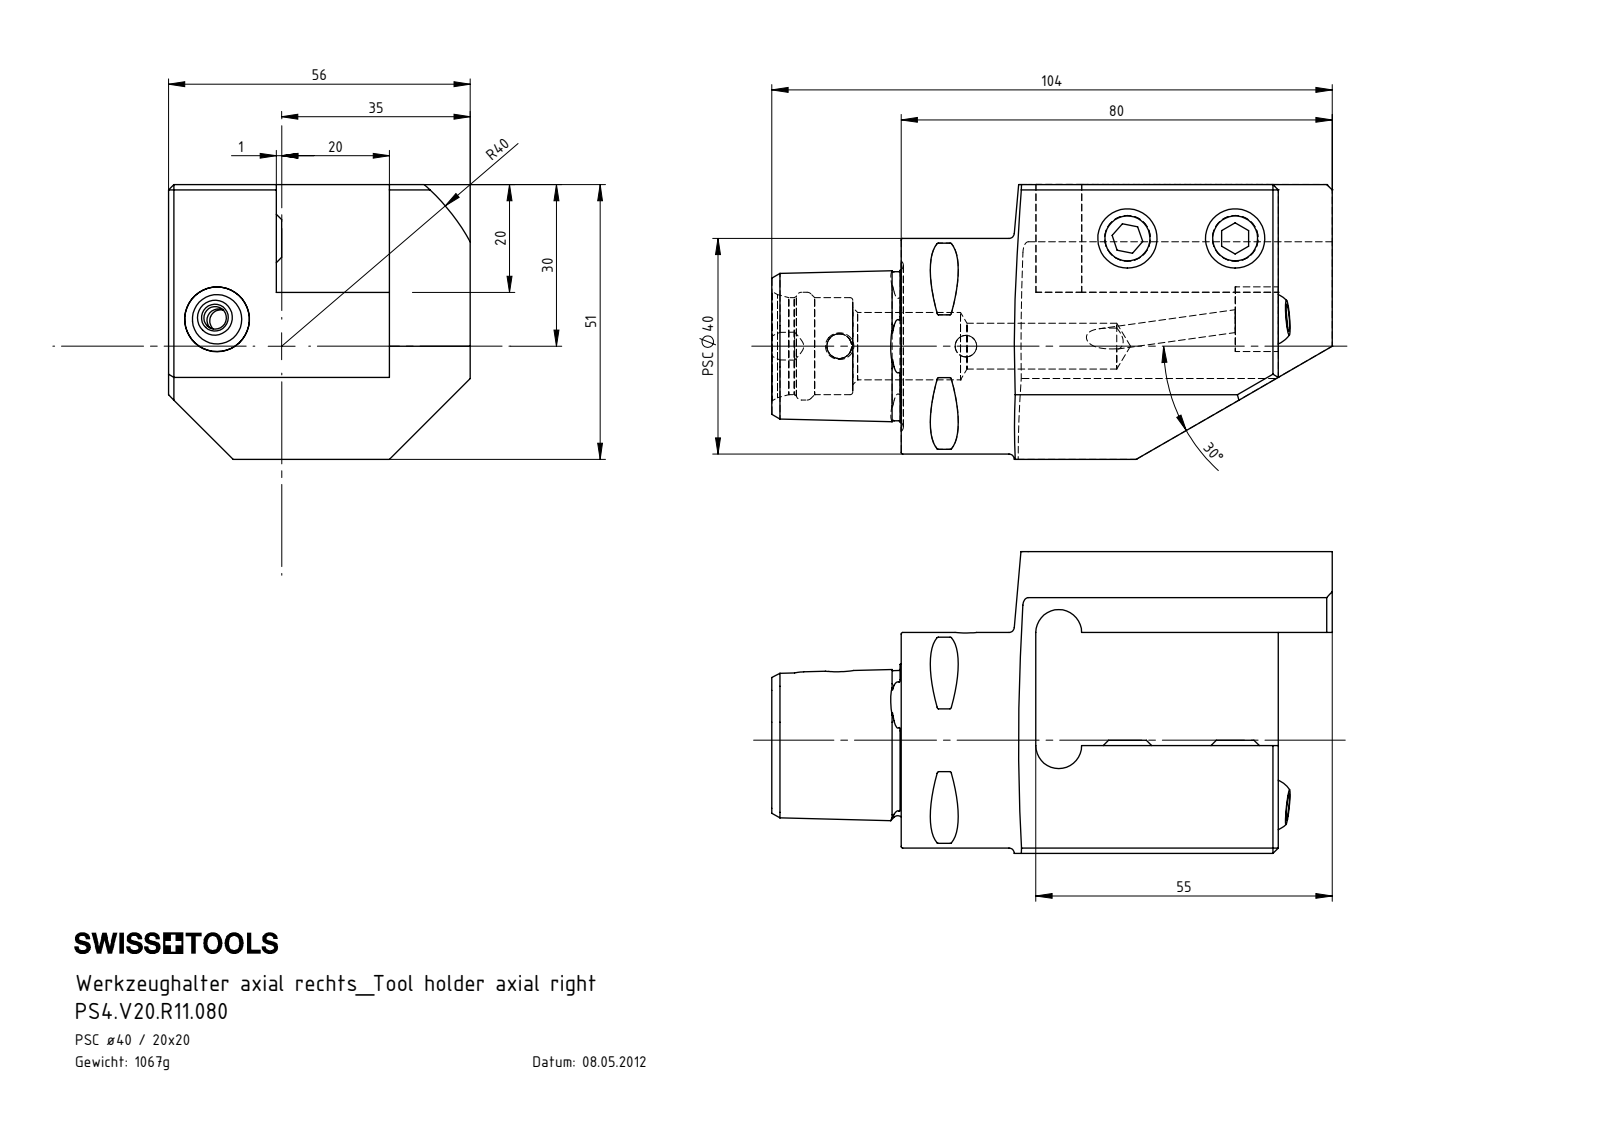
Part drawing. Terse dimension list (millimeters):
name: ISO 4026 - M10 x 20; PS4.V20.R11.080; KU1-U12.001.010; PS4-V20.R11.080_A (+2 more)
written by: SolidWorks 2017 (AUTOMOTIVE_DESIGN)
unit: mm
bodies: 5 solids, 215 faces (59 planar, 49 cylindrical, 107 other)
size: 104 × 56 × 51
volume: 135 810 mm³; area: 27 964 mm²
holes: 3× ⌀8.5, 2× ⌀4.2, 1× ⌀4, 1× ⌀4.6, 1× ⌀7, 1× ⌀12, 1× ⌀12.5, 1× ⌀18, 1× ⌀20
bosses: 2× ⌀10, 1× ⌀40
rounds: 8× R0.3, 2× R5, 1× R3, 1× R40
face distances: 20, 56, 15, 41, 21, 51, 31, 36, 55, 70
hole spacings: 13, 20, 23.5, 36.06, 53.85, 57.12, 76.17
